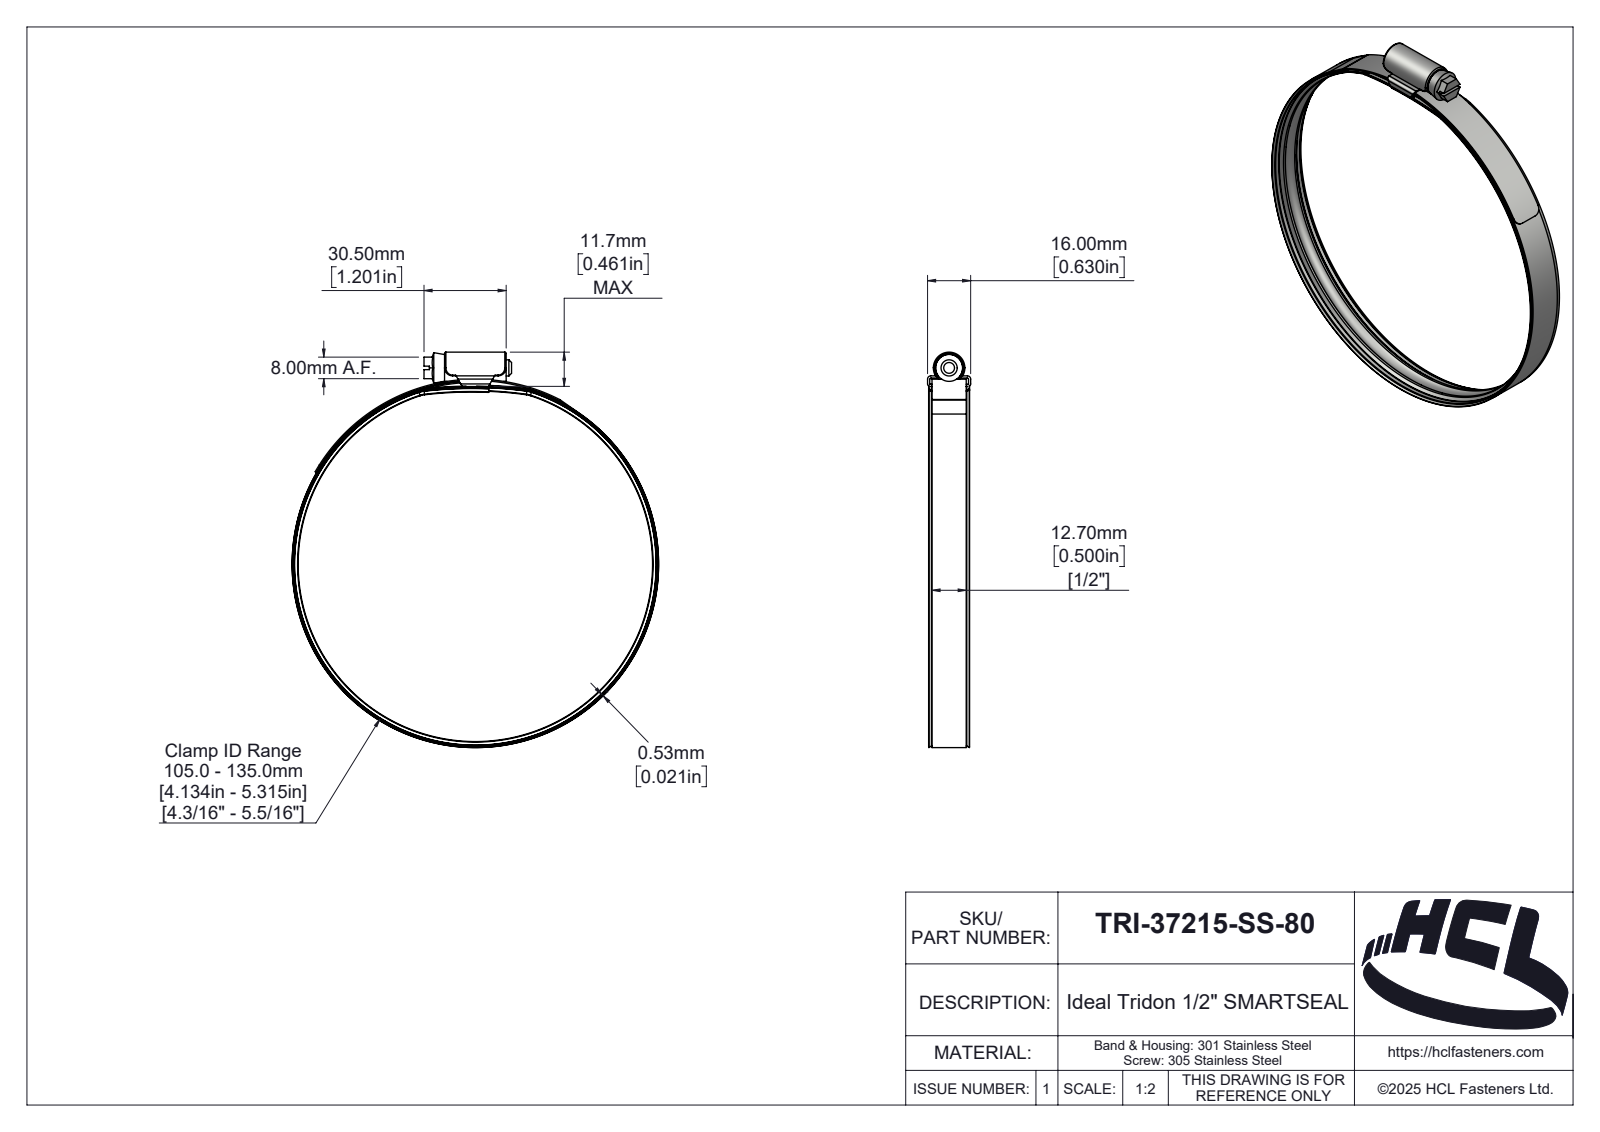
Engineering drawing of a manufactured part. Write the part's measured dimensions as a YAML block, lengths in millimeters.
part_name: "TRI-37215-SS-80"
step_written_by: "SolidWorks 2025 (AUTOMOTIVE_DESIGN)"
units: millimeters
bodies: {solids: 4, faces: 418, planar: 42, cylindrical: 119, other: 257}
overall_size: [146.73, 136.06, 16]
volume: 7861
surface_area: 30874
round_holes:
  - {diameter: 134.4, count: 1}
  - {diameter: 135, count: 1}
round_bosses_or_shafts:
  - {diameter: 136.06, count: 1}
  - {diameter: 134.8, count: 1}
  - {diameter: 10, count: 1}
  - {diameter: 6, count: 1}
partial_cylinders:
  - {radius: 0.5, count: 6}
  - {radius: 3, count: 4}
  - {radius: 0.1, count: 2}
  - {radius: 0.9, count: 2}
  - {radius: 1.2, count: 2}
  - {radius: 9.9, count: 2}
  - {radius: 10.1, count: 2}
  - {radius: 0.46, count: 1}
face_to_face_distances: [12.7, 0.8, 3.1, 0.53, 2.3, 30.5, 3.9, 1.65, 14.35, 15.2]
